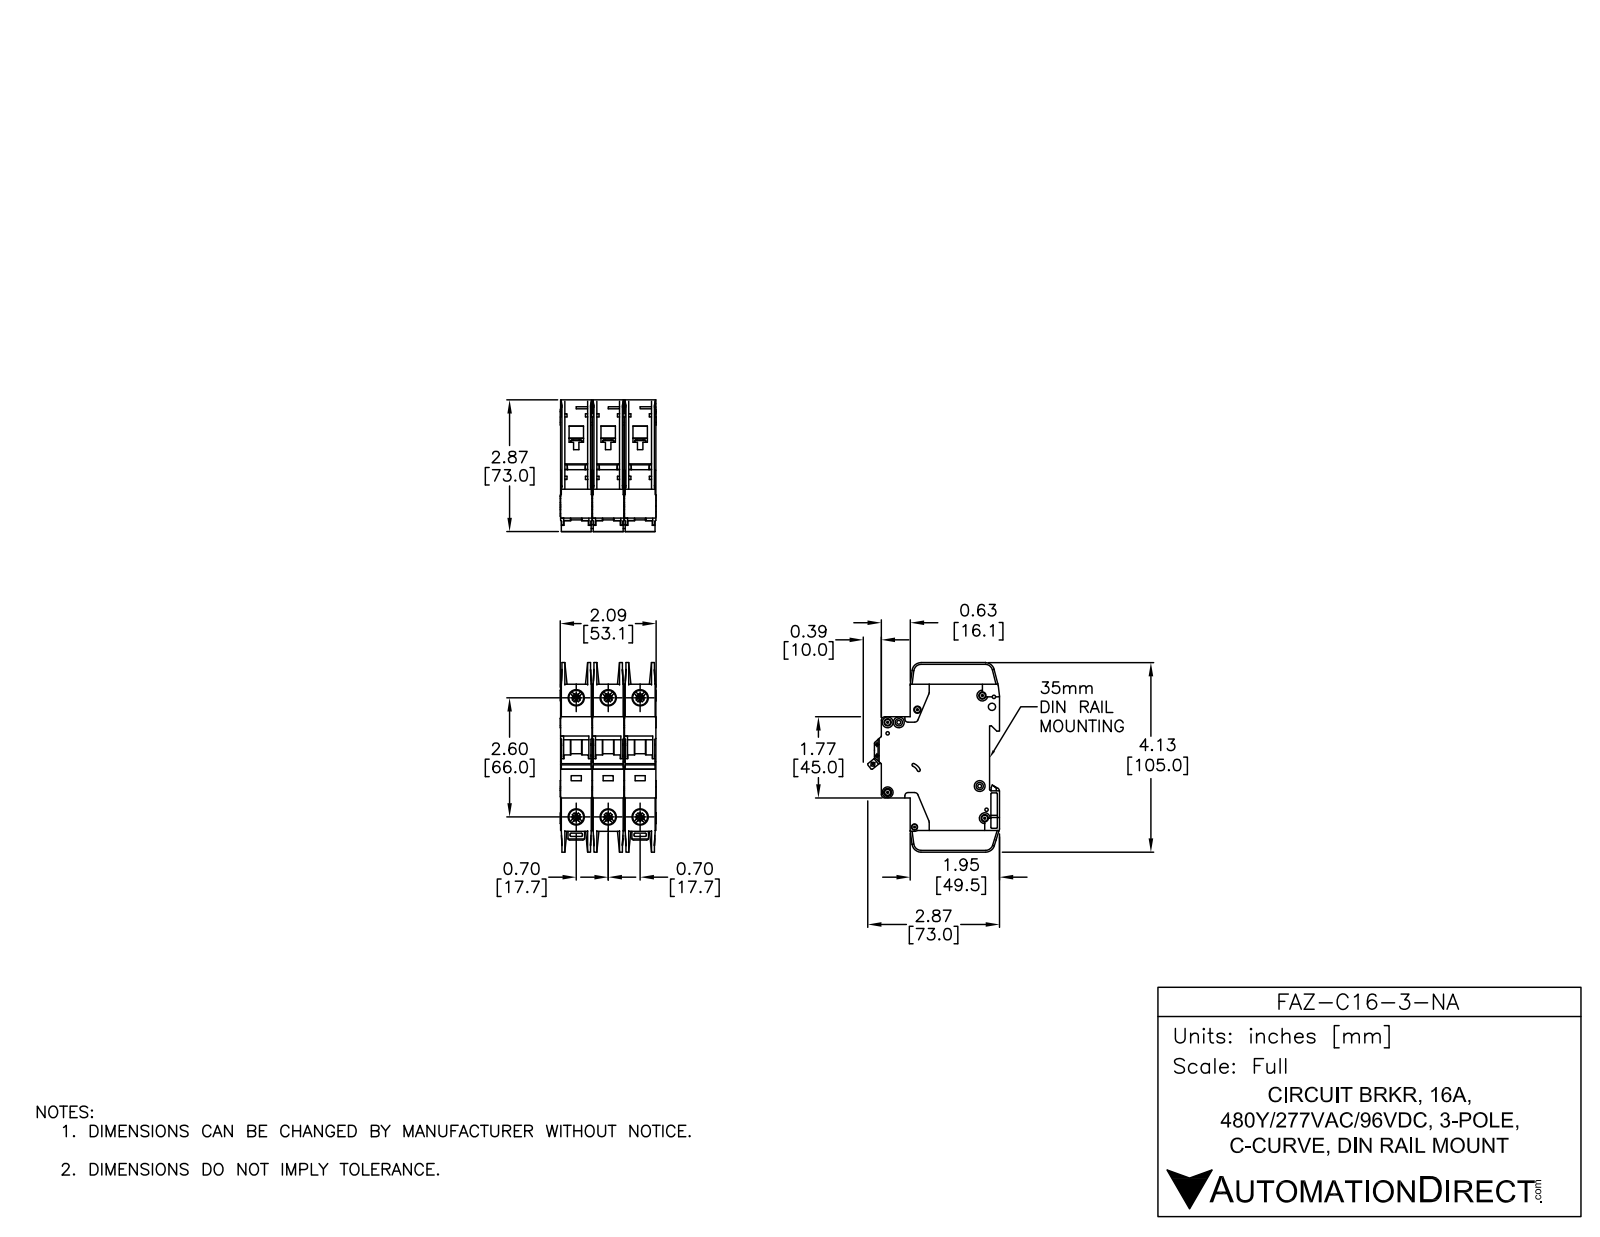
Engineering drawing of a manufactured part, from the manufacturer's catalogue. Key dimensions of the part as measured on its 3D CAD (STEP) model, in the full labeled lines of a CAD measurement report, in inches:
Part name (STEP PRODUCT): FAZ-C16-3-NA
STEP written by: SolidWorks 2014 (AUTOMOTIVE_DESIGN)
Units: inches
Bodies: 9 solids, 2352 faces (1227 planar, 789 cylindrical, 336 other)
Overall size (bounding box): 4.134 × 2.876 × 2.091
Volume: 14.22 in³ · Surface area: 115 in²
Round holes (diameter × count): ⌀0.142 ×7, ⌀0.281 ×6, ⌀0.323 ×6, ⌀0.043 ×2, ⌀0.059 ×2, ⌀0.157 ×2, ⌀0.075 ×1, ⌀0.085 ×1, ⌀0.087 ×1, ⌀0.1 ×1, ⌀0.13 ×1, ⌀0.134 ×1
Round bosses / shafts (diameter × count): ⌀0.236 ×7, ⌀0.098 ×3
Partial cylindrical surfaces — rounded edges, fillets, slot ends (radius × count): R0.01 ×65, R0.02 ×30, R0.039 ×26, R0.079 ×14, R0.071 ×5, R0.197 ×5, R0.157 ×4, R0.008 ×2
Main face-to-face distances: 0.697, 1.394, 0.689, 1.386, 0.028, 0.593, 0.096, 0.069, 0.62, 0.524
Hole centre spacings: 0.697, 2.69, 2.598, 0.244, 1.394, 2.948, 0.204, 0.24
